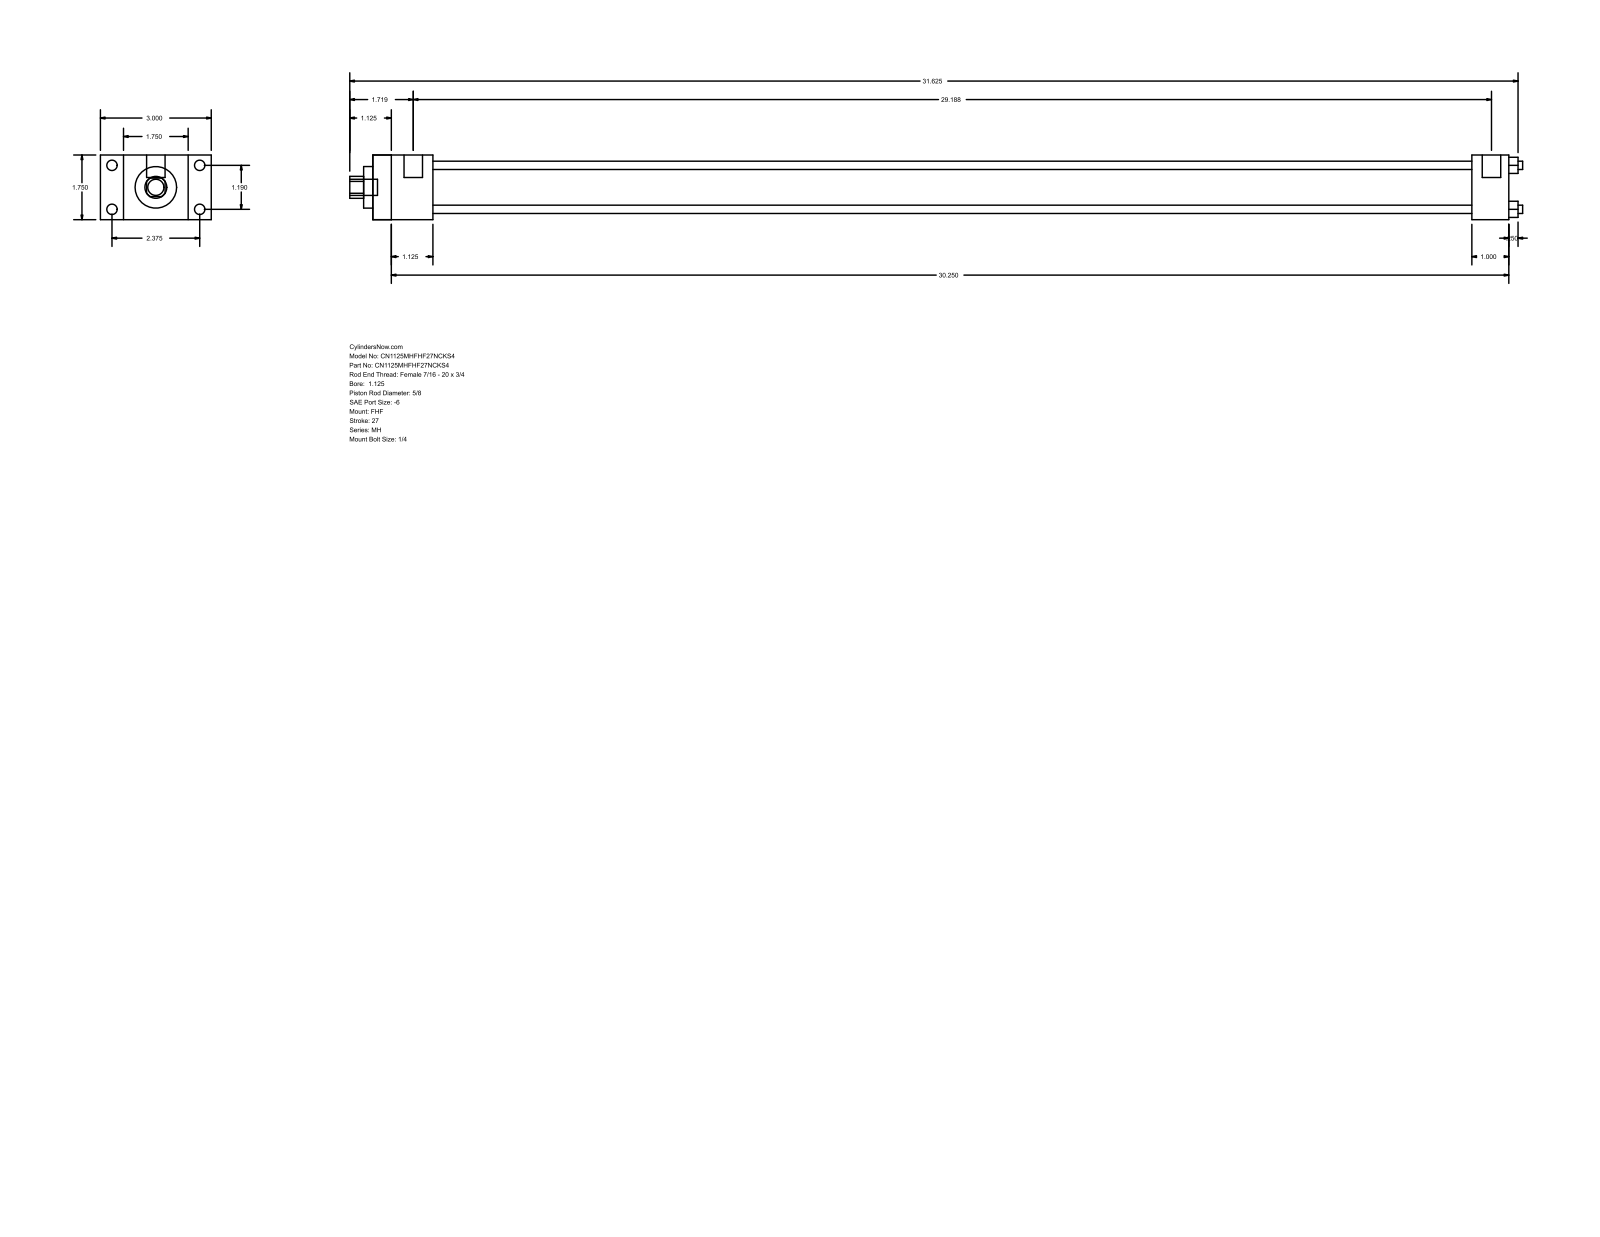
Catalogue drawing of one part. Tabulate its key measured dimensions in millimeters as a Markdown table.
| quantity | value |
| --- | --- |
| part name | MH_FHF__0112_0.625 |
| STEP written by | GSSL Pune (CONFIG_CONTROL_DESIGN) |
| units | millimeters |
| bodies | 0 solids, 88 faces (60 planar, 28 cylindrical, 0 other) |
| overall size | 806.45 × 76.2 × 44.45 |
| round holes (diameter × count) | 5.71 × 4, 15.88 × 1, 28.57 × 1, 34.92 × 1 |
| round bosses / shafts (diameter × count) | 7.14 × 4, 5.56 × 4, 12.7 × 2, 11.11 × 1 |
| partial cylindrical surfaces (radius × count) | 7.54 × 1 |
| main face-to-face distances | 44.46, 15.87, 60.33, 41.27, 76.2, 781.04, 739.77, 755.64, 714.37, 25.4 |
| hole center spacings | 21.37, 30.22, 42.74 |
